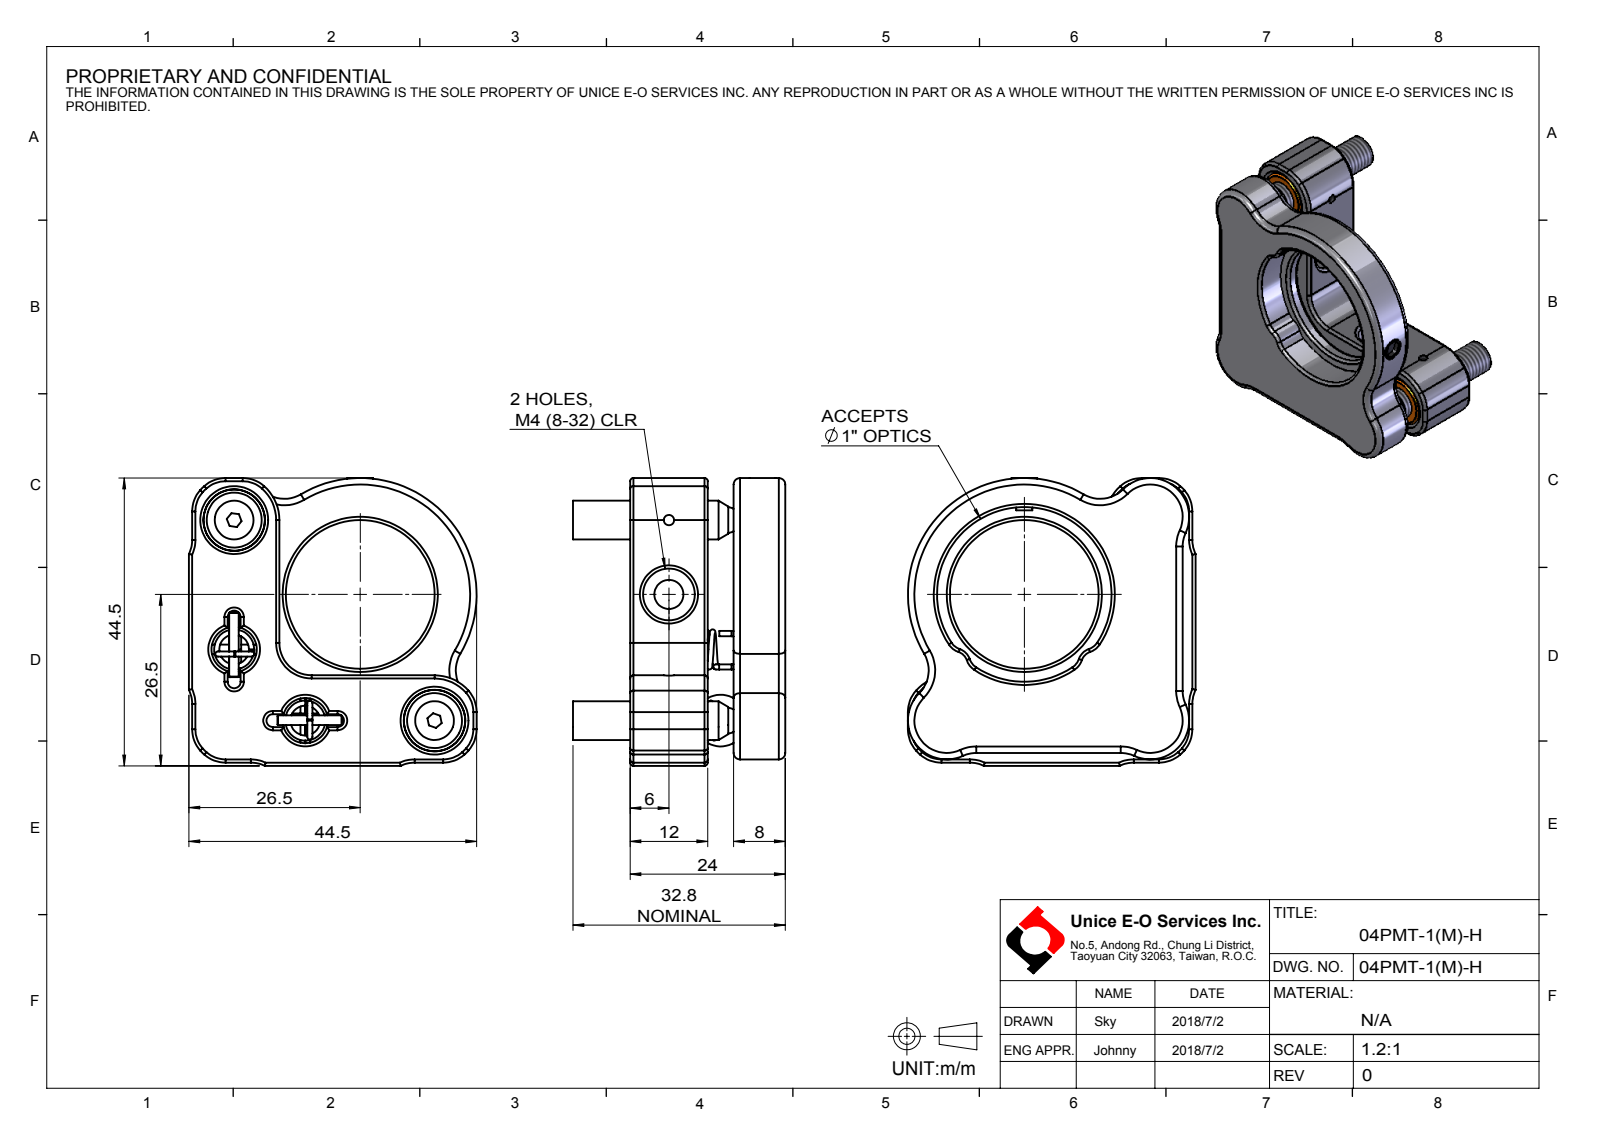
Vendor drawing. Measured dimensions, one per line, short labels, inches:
name: 04PMT-1(M)-H
written by: SolidWorks 2016 (AUTOMOTIVE_DESIGN)
unit: in
bodies: 0 solids, 381 faces (69 planar, 153 cylindrical, 159 other)
size: 1.752 × 1.752 × 1.293
holes: 2× ⌀0.039, 2× ⌀0.063, 2× ⌀0.067, 2× ⌀0.177, 2× ⌀0.276, 2× ⌀0.315, 1× ⌀0.13, 1× ⌀0.236, 1× ⌀0.906, 1× ⌀1.063
bosses: 7× ⌀0.031, 5× ⌀0.059, 1× ⌀0.236, 1× ⌀0.157, 1× ⌀0.098
rounds: 20× R0.02, 19× R0.197, 8× R0.039, 6× R0.098, 4× R0.03, 3× R0.236, 3× R0.276, 1× R0.059
face distances: 0.472, 0.315, 0.63, 0.157, 0.945, 0.079, 0.551, 0.059, 0.531, 0.02
hole spacings: 0.453, 0.679, 0.837, 0.984, 0.335, 0.571, 0.613, 0.729
